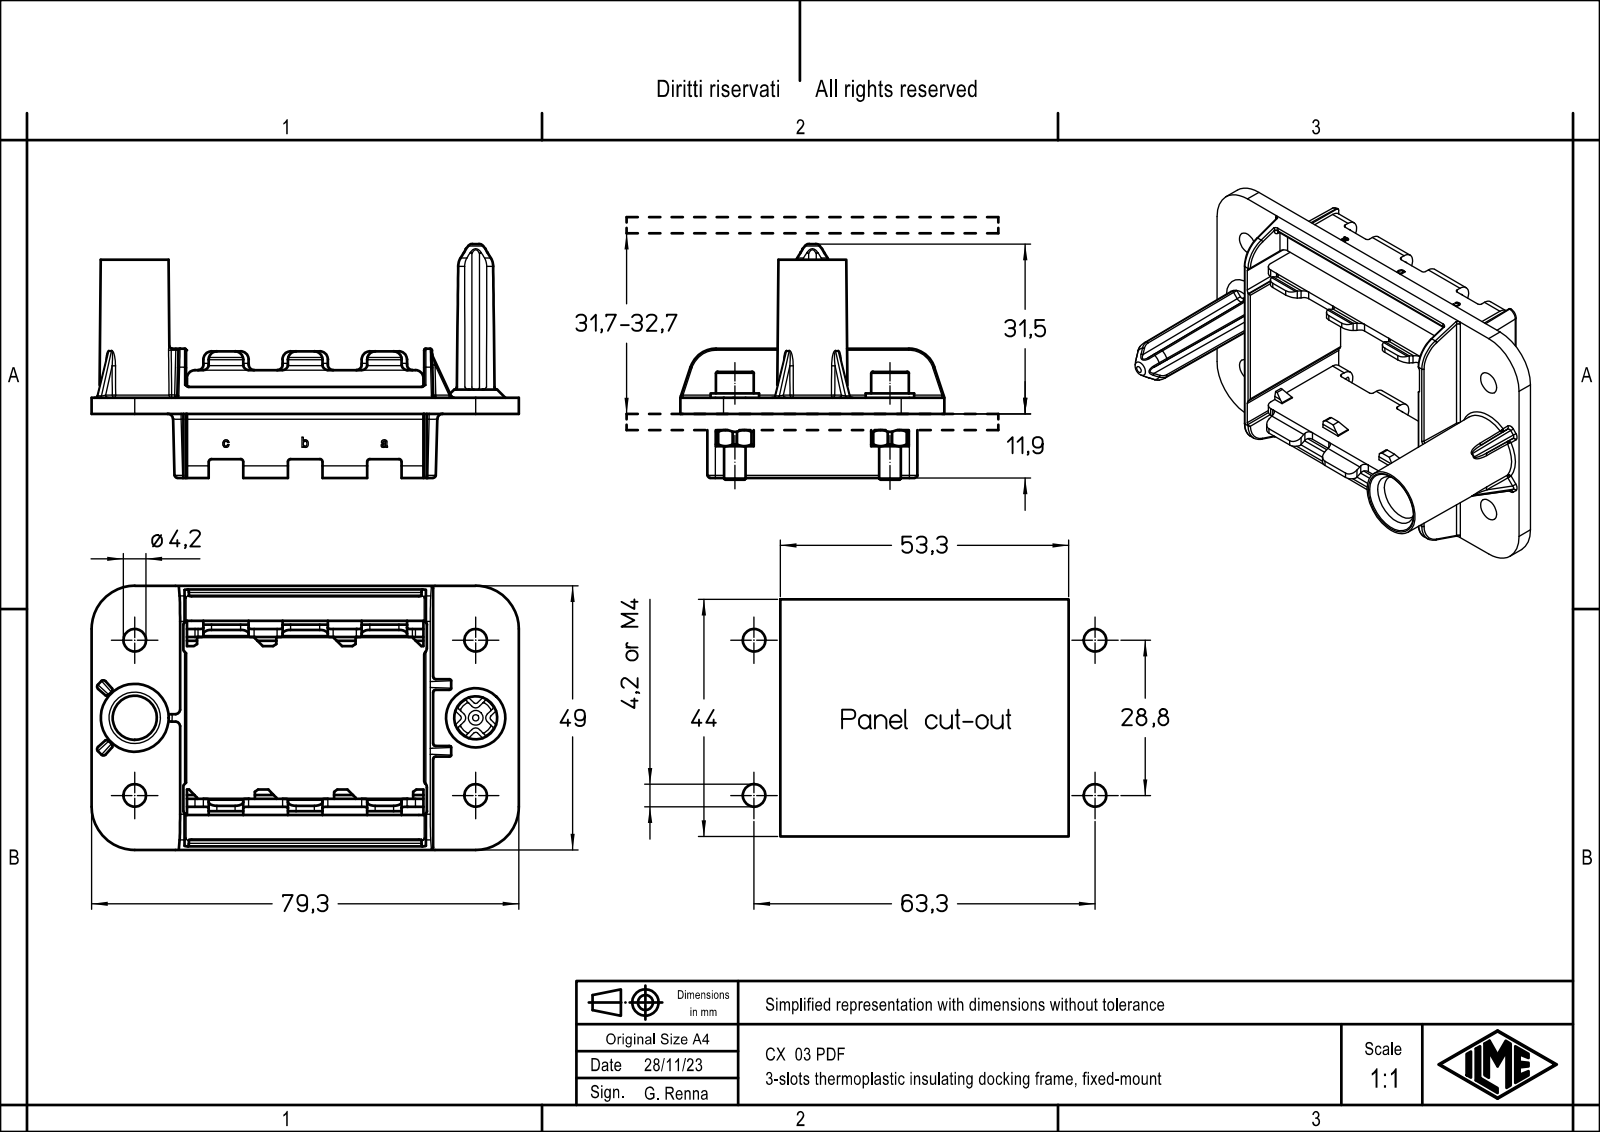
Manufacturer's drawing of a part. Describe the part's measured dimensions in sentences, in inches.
The part is named "CX 03 PDF". Its 3-D file was written by "Creo Elements/Direct Modeling 20.1B 02-Apr-2019 (C) Parametric Technology GmbH (AUTOMOTIVE_DESIGN)". It is 1 solid with 404 faces: 255 planar, 129 cylindrical and 20 other. Overall it measures 3.122 by 1.929 by 1.709 inches. Its volume is 1.007 cubic inches and its surface area 27.76 square inches. Round holes: 4 of diameter 0.165. Partial cylindrical surfaces (rounded edges, fillets, slot ends): 18 of radius 0.039, 18 of radius 0.059, 15 of radius 0.004, 12 of radius 0.02, 4 of radius 0.315, 2 of radius 0.03, 2 of radius 0.079, 2 of radius 0.089. The main face-to-face distances are 0.118, 0.059, 1.358, 1.299, 1.24, 1.417, 0.177, 1.476, 1.904, 0.02. The hole center spacings are 1.134, 2.492, 2.738.
